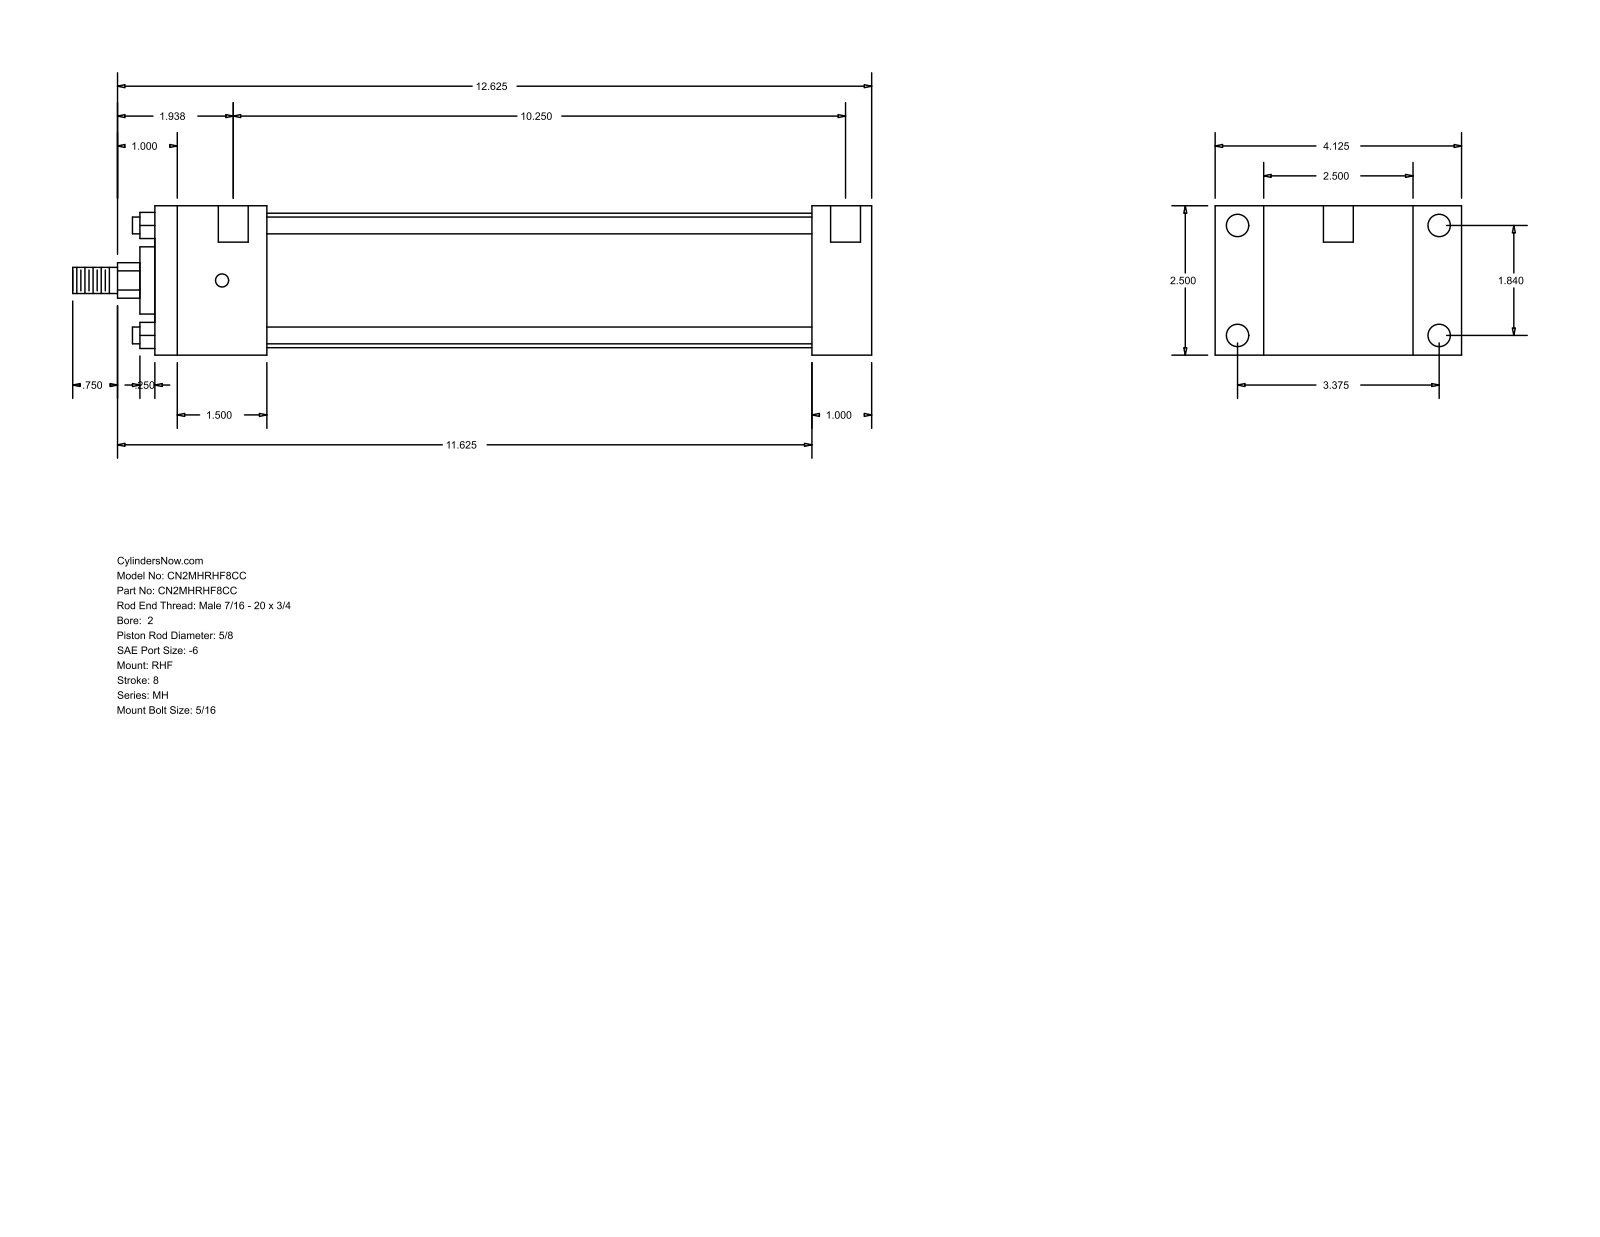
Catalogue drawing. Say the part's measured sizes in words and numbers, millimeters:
The part is named "MH_RHF__0200_0.625". Its 3-D file was written by "GSSL Pune (CONFIG_CONTROL_DESIGN)". It is 0 solids with 88 faces: 60 planar, 28 cylindrical and 0 other. Overall it measures 339.73 by 104.78 by 63.5 millimeters. Round holes: 4 of diameter 5.56, 4 of diameter 9.53, 2 of diameter 12.7. Round bosses or shafts: 4 of diameter 7.14, 1 of diameter 57.15, 1 of diameter 28.57, 1 of diameter 15.88, 1 of diameter 11.11. Partial cylindrical surfaces (rounded edges, fillets, slot ends): 1 of radius 7.54. The main face-to-face distances are 63.5, 25.41, 20.64, 84.14, 279.39, 304.8, 104.78, 47.62, 231.77, 257.18. The hole center spacings are 46.74, 85.72, 97.63, 268.29, 3.18, 4.76, 260.35, 263.53.
